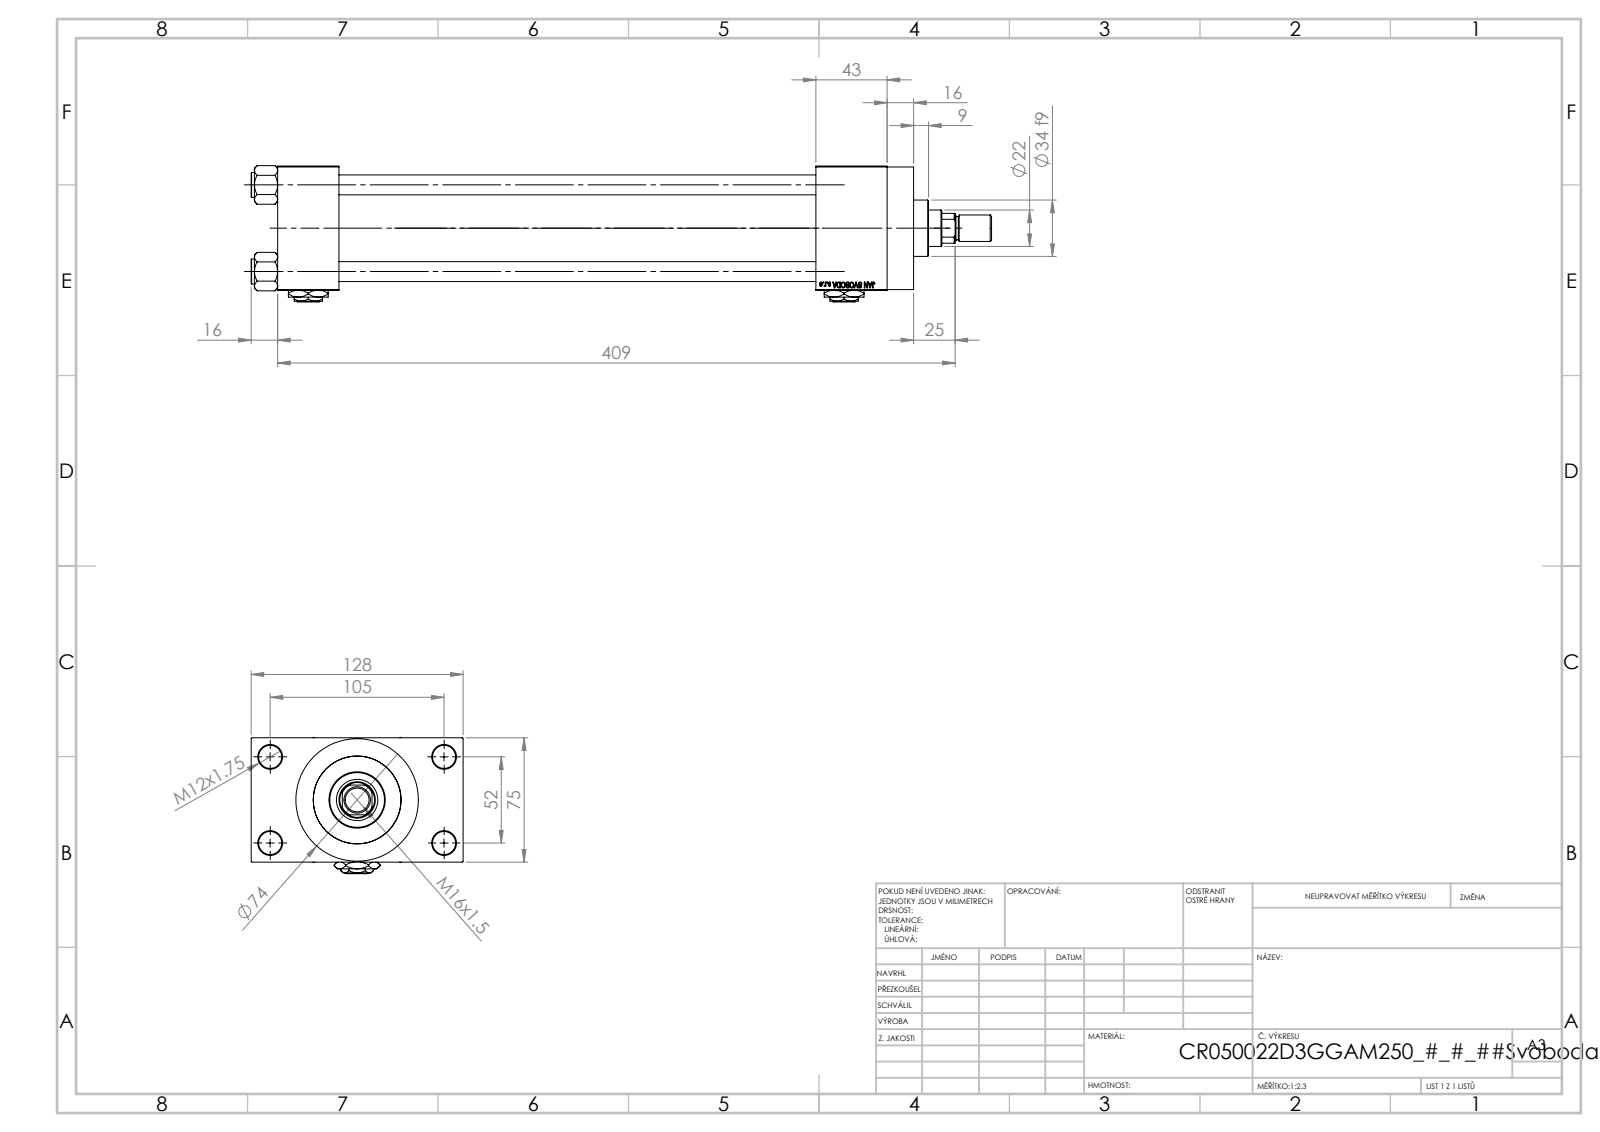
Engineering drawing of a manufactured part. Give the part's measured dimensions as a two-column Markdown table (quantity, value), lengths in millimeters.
| quantity | value |
| --- | --- |
| part name | V215_VC_A; V215CR_D_TYCINKA; Zatka_pro_OIL_PORT; V215CR_D_Body (+3 more) |
| STEP written by | SolidWorks 2019 (CONFIG_CONTROL_DESIGN) |
| units | millimeters |
| bodies | 14 solids, 1219 faces (549 planar, 104 cylindrical, 566 other) |
| overall size | 447 × 128 × 82.27 |
| volume | 1 113 000 mm³ |
| surface area | 297 896 mm² |
| round holes (diameter × count) | 12 × 4, 14 × 4, 7 × 2, 20.96 × 2, 30 × 2, 10.5 × 1, 22 × 1, 25 × 1, 41 × 1, 50 × 1, 53 × 1 |
| round bosses / shafts (diameter × count) | 15 × 4, 74 × 1, 56 × 1, 34 × 1, 16 × 1, 14 × 1 |
| partial cylindrical surfaces (radius × count) | 10.5 × 1 |
| main face-to-face distances | 75, 288, 37, 325, 26.5, 101.5, 368, 331, 43, 16 |
| hole center spacings | 26.35, 36.98, 52.3, 58.43, 58.59, 78.65, 94.37, 52 |
